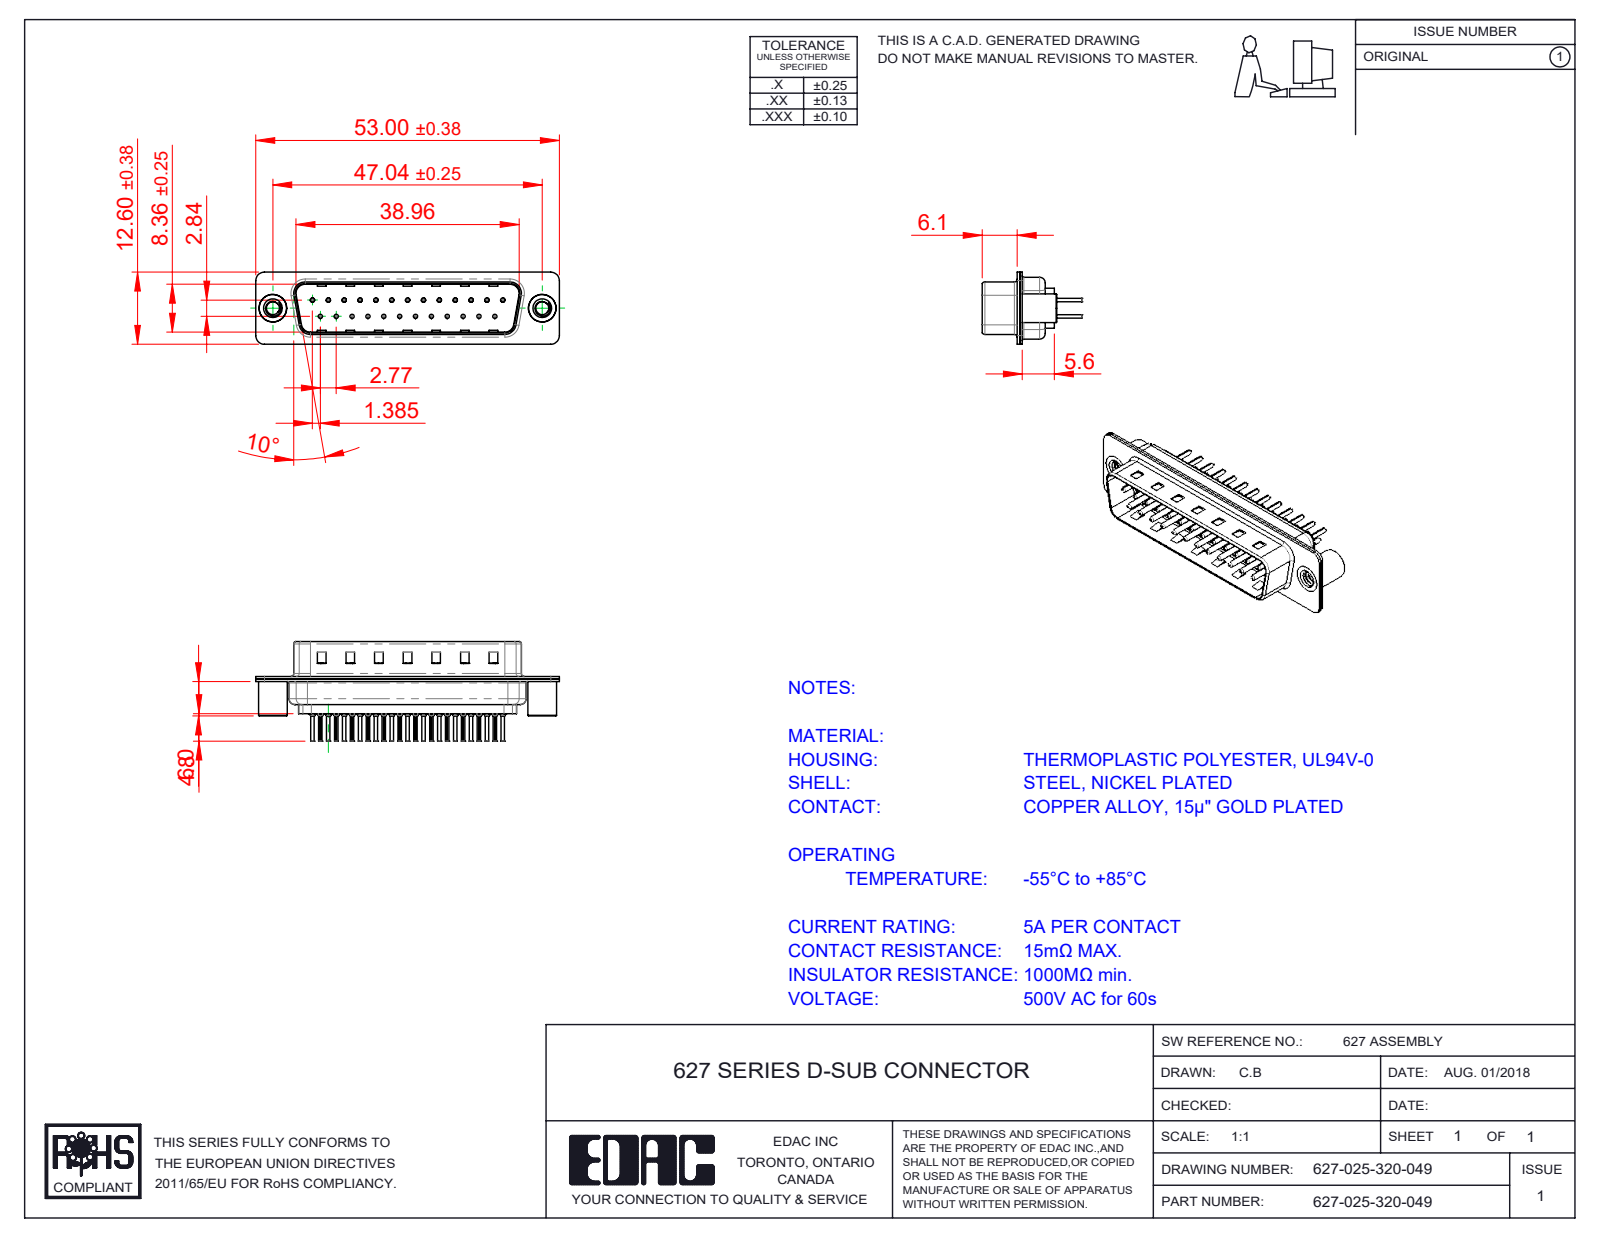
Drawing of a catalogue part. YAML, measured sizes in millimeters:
part_name: "627-025-320-049; 627 Contact Row 2_20L; 627 Shell Rear_25 Contacts; 627 Housing_25 LP (+3 more)"
step_written_by: "SolidWorks 2020 (CONFIG_CONTROL_DESIGN)"
units: millimeters
bodies: {solids: 30, faces: 2848, planar: 771, cylindrical: 1082, other: 995}
overall_size: [53, 17.3, 12.6]
volume: 2779
surface_area: 7995
round_holes:
  - {diameter: 0.2, count: 25}
  - {diameter: 0.35, count: 25}
  - {diameter: 1.1, count: 25}
  - {diameter: 1.6, count: 25}
  - {diameter: 2.26, count: 2}
  - {diameter: 4, count: 2}
  - {diameter: 4.8, count: 2}
round_bosses_or_shafts:
  - {diameter: 2, count: 25}
  - {diameter: 1.5, count: 25}
  - {diameter: 0.75, count: 25}
  - {diameter: 0.6, count: 25}
  - {diameter: 5, count: 2}
  - {diameter: 4.9, count: 2}
partial_cylinders:
  - {radius: 0.1, count: 50}
  - {radius: 1.5, count: 16}
  - {radius: 2, count: 12}
  - {radius: 0.5, count: 8}
  - {radius: 1.6, count: 8}
  - {radius: 0.25, count: 4}
  - {radius: 0.6, count: 4}
  - {radius: 0.65, count: 4}
face_to_face_distances: [0.4, 0.45, 0.82, 9.58, 8.76, 0.9, 1.5, 6.5, 1.4, 6.05]
hole_center_spacings: [3.16, 8.31, 2.77, 5.54, 11.08, 16.62, 5.03, 5.04]
